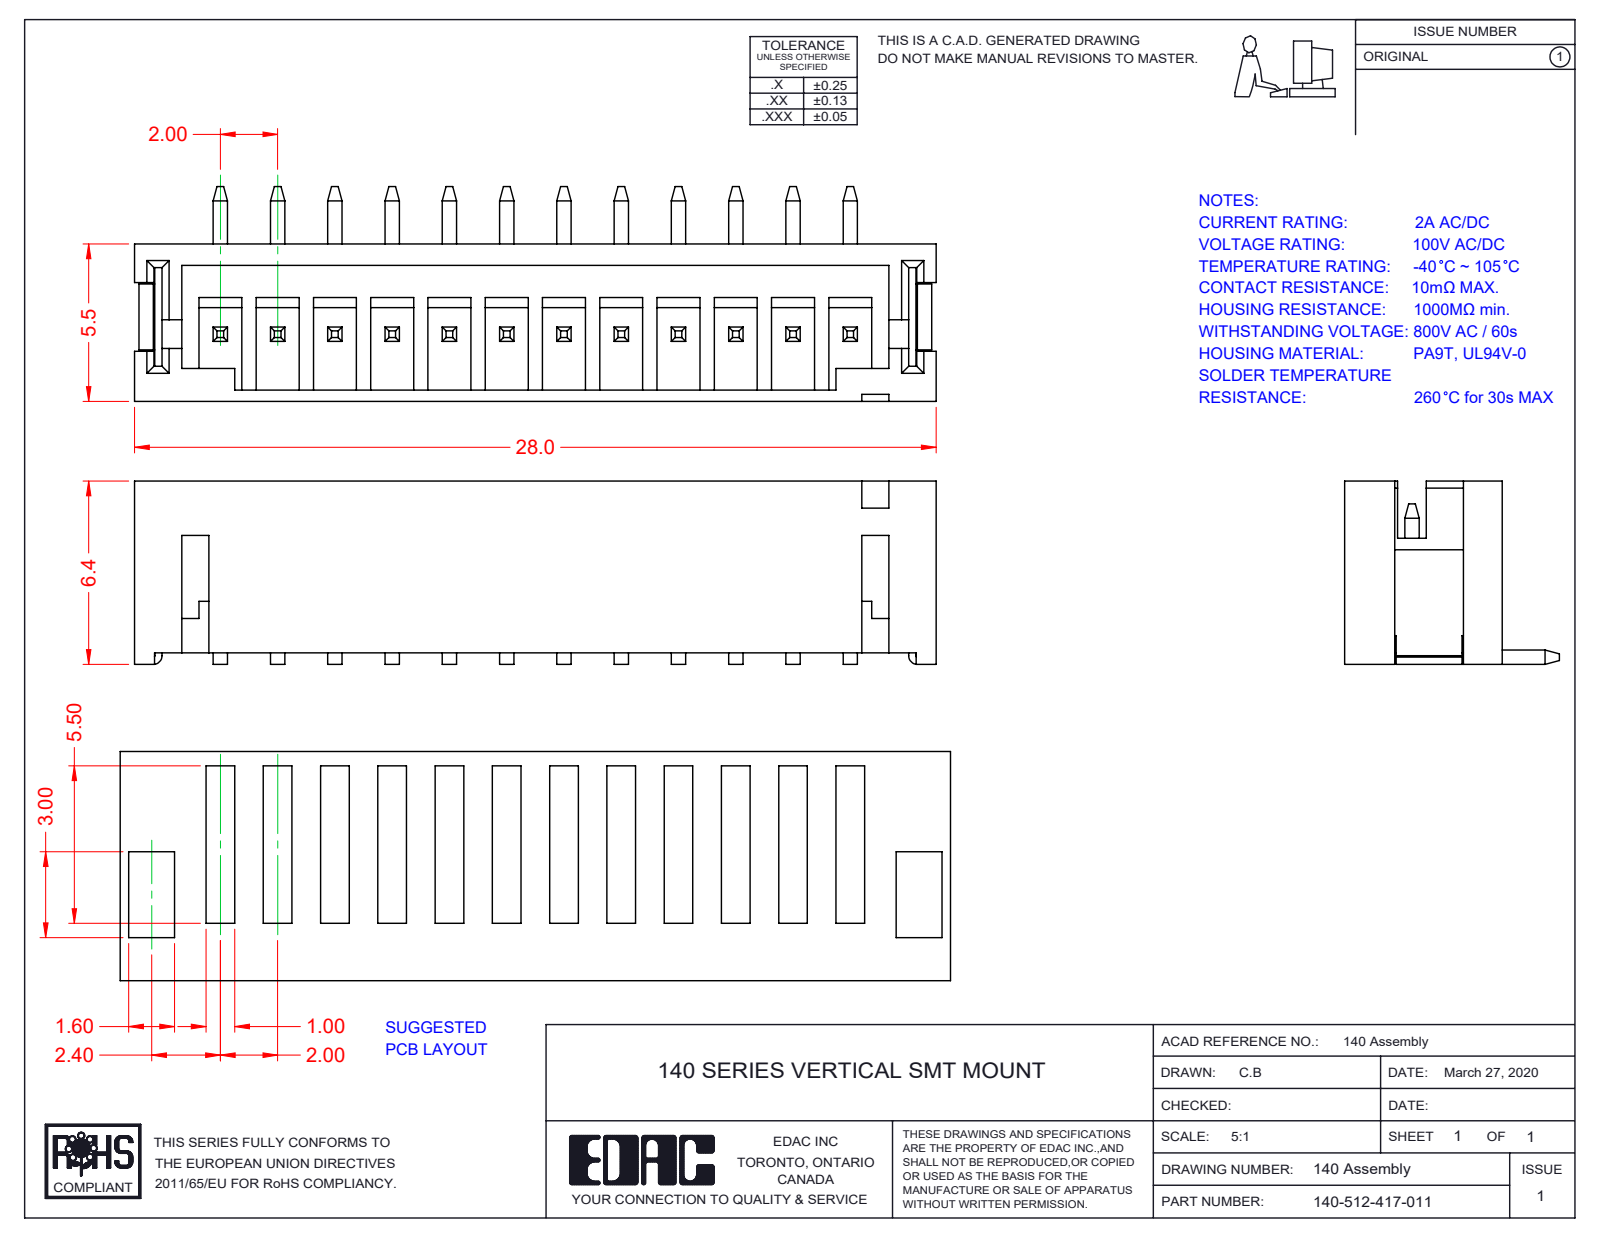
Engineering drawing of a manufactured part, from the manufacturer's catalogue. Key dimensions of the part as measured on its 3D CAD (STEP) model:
Part name (STEP PRODUCT): V SMT Pad; V SMT Contact; V SMT Housing_512; 140-512-417-011
STEP written by: SolidWorks 2016 (CONFIG_CONTROL_DESIGN)
Units: millimetres
Bodies: 15 solids, 556 faces (528 planar, 28 cylindrical, 0 other)
Overall size (bounding box): 28 × 7.5 × 6.4
Volume: 403 mm³ · Surface area: 1 459 mm²
Partial cylindrical surfaces — rounded edges, fillets, slot ends (radius × count): R0.3 ×2, R0.55 ×1
Main face-to-face distances: 5.5, 0.75, 0.4, 4.75, 4.35, 0.5, 5.1, 0.6, 0.55, 1.7
